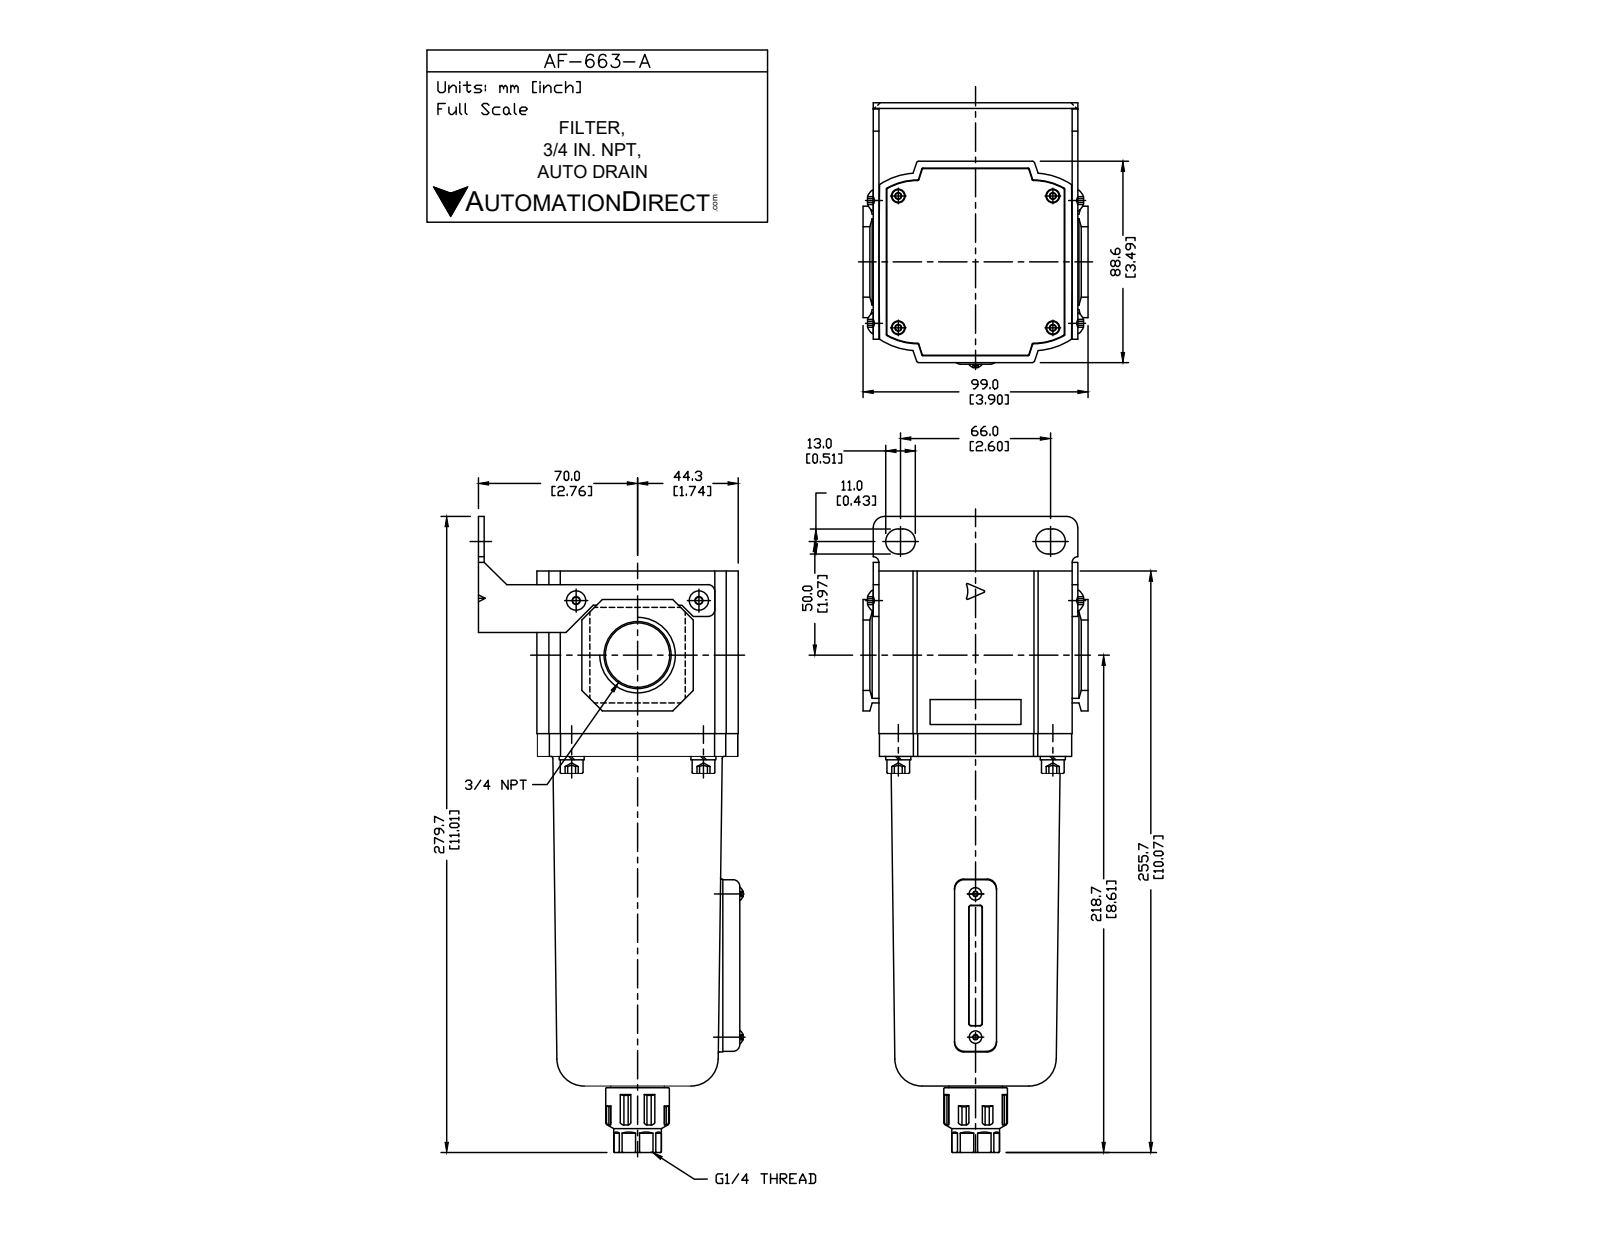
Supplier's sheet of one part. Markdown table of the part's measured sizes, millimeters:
| quantity | value |
| --- | --- |
| part name | AF-663-A |
| STEP written by | SolidWorks 2015 (CONFIG_CONTROL_DESIGN) |
| units | millimeters |
| bodies | 8 solids, 384 faces (233 planar, 88 cylindrical, 63 other) |
| overall size | 280 × 116.49 × 99 |
| volume | 1 247 000 mm³ |
| surface area | 118 905 mm² |
| round holes (diameter × count) | 5.5 × 2, 11.45 × 1, 23.01 × 1 |
| round bosses / shafts (diameter × count) | 10 × 4, 74.5 × 1, 28 × 1, 21 × 1 |
| partial cylindrical surfaces (radius × count) | 3 × 10, 9.5 × 8, 0.5 × 6, 2 × 5, 0.3 × 4, 1 × 4, 5.5 × 4, 29.7 × 4 |
| main face-to-face distances | 2.5, 71.5, 85, 92, 25.7, 23.2, 114.3, 111.8, 88.6, 94.5 |
| hole center spacings | 36.12, 54 |
